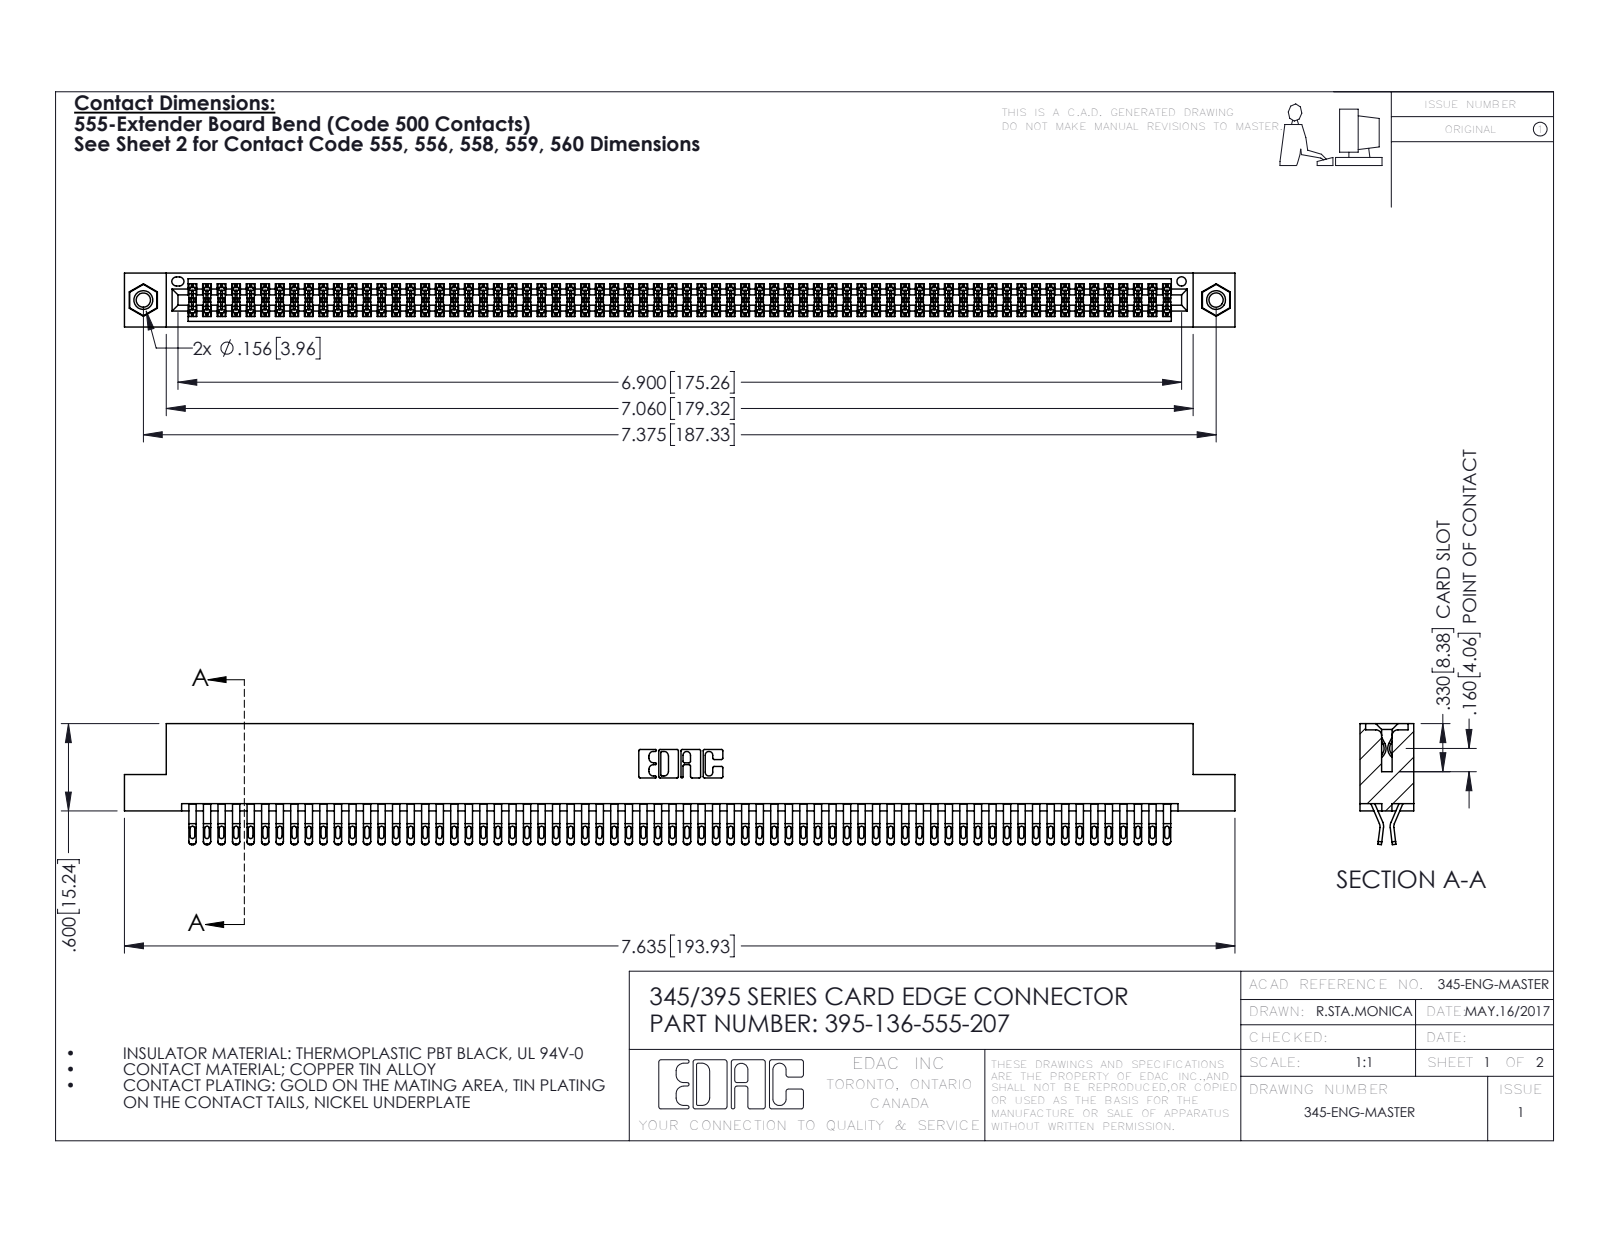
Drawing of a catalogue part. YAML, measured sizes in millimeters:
part_name: "395-136-555-207; 345-250-001_345-250-005-103; 345-292-001_555 Tail; 345 Part_Flush Mounting Lugs - 0.156 Dia-TI"
step_written_by: "SolidWorks 2016 (CONFIG_CONTROL_DESIGN)"
units: millimeters
bodies: {solids: 139, faces: 7802, planar: 4328, cylindrical: 3458, other: 16}
overall_size: [193.9, 21.1, 9.4]
volume: 19470
surface_area: 30670
round_holes:
  - {diameter: 2.5, count: 2}
  - {diameter: 3.2, count: 2}
  - {diameter: 4, count: 2}
  - {diameter: 1.6, count: 1}
round_bosses_or_shafts:
  - {diameter: 3.9, count: 2}
partial_cylinders:
  - {radius: 0.4, count: 340}
  - {radius: 0.5, count: 272}
  - {radius: 0.2, count: 204}
  - {radius: 0.3, count: 22}
  - {radius: 0.2, count: 6}
  - {radius: 0.8, count: 6}
  - {radius: 0.7, count: 3}
  - {radius: 0.3, count: 2}
face_to_face_distances: [1.8, 7.6, 0.6, 9.4, 5.1, 2.5, 6.9, 5.7, 4.4, 3.8]
hole_center_spacings: [6.9, 181.3, 187.3]
